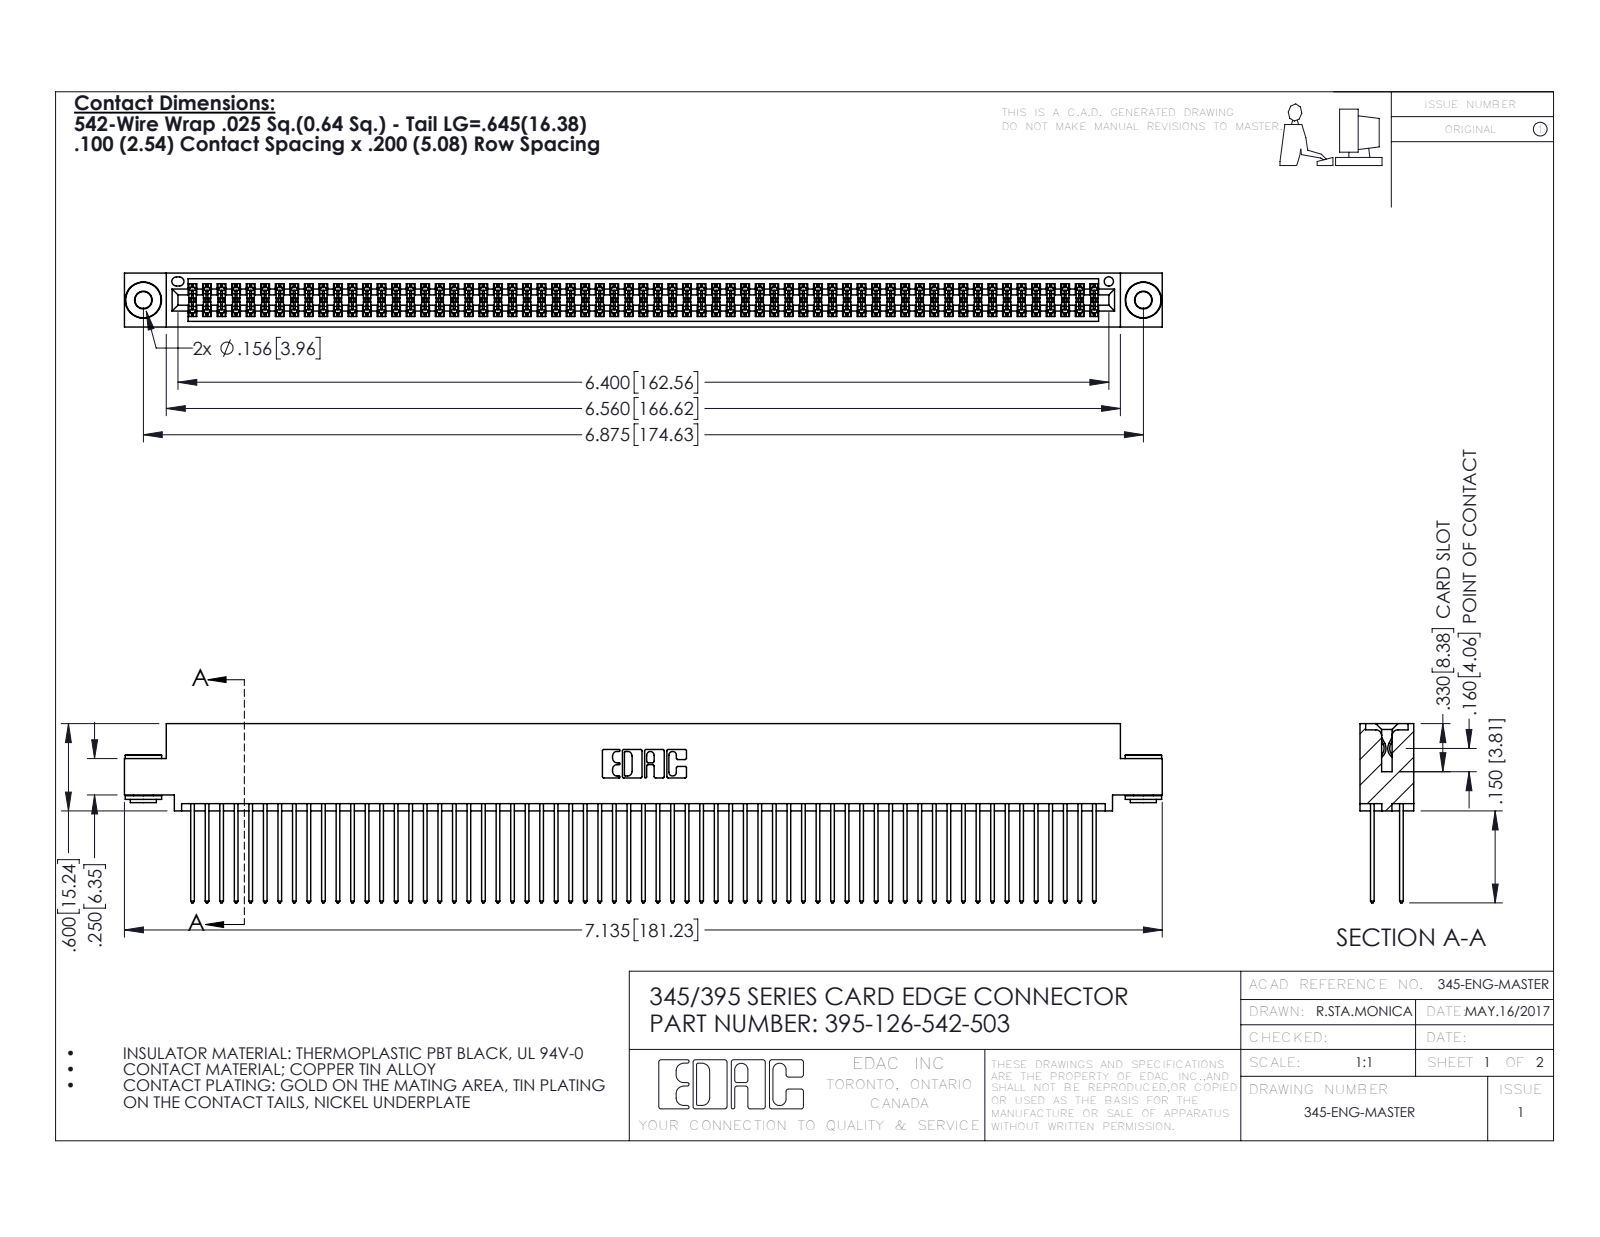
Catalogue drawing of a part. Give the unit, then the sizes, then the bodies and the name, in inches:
Units: inches
Overall size (bounding box): 7.135 × 1.232 × 0.37
Round holes (diameter × count): ⌀0.116 ×2, ⌀0.156 ×2, ⌀0.064 ×1
Round bosses / shafts (diameter × count): ⌀0.25 ×2, ⌀0.18 ×2, ⌀0.136 ×2
Partial cylindrical surfaces — rounded edges, fillets, slot ends (radius × count): R0.006 ×189, R0.01 ×126, R0.01 ×22, R0.007 ×6, R0.031 ×6, R0.026 ×3, R0.014 ×2, R0.019 ×2
Main face-to-face distances: 0.072, 0.298, 0.2, 0.025, 0.098, 0.272, 0.225, 0.37, 0.175, 0.149
Hole centre spacings: 0.27, 6.639, 6.875
Volume: 1.119 in³ · Surface area: 47.35 in²
Bodies: 129 solids, 6468 faces (4252 planar, 2208 cylindrical, 8 other)
Part name (STEP PRODUCT): 345-250-002_345-250-002-102; 345 Part_0.110 Offset - 0.156 Dia-TH; 395-126-542-503; 345-292-001_345-293-142
STEP written by: SolidWorks 2016 (CONFIG_CONTROL_DESIGN)
